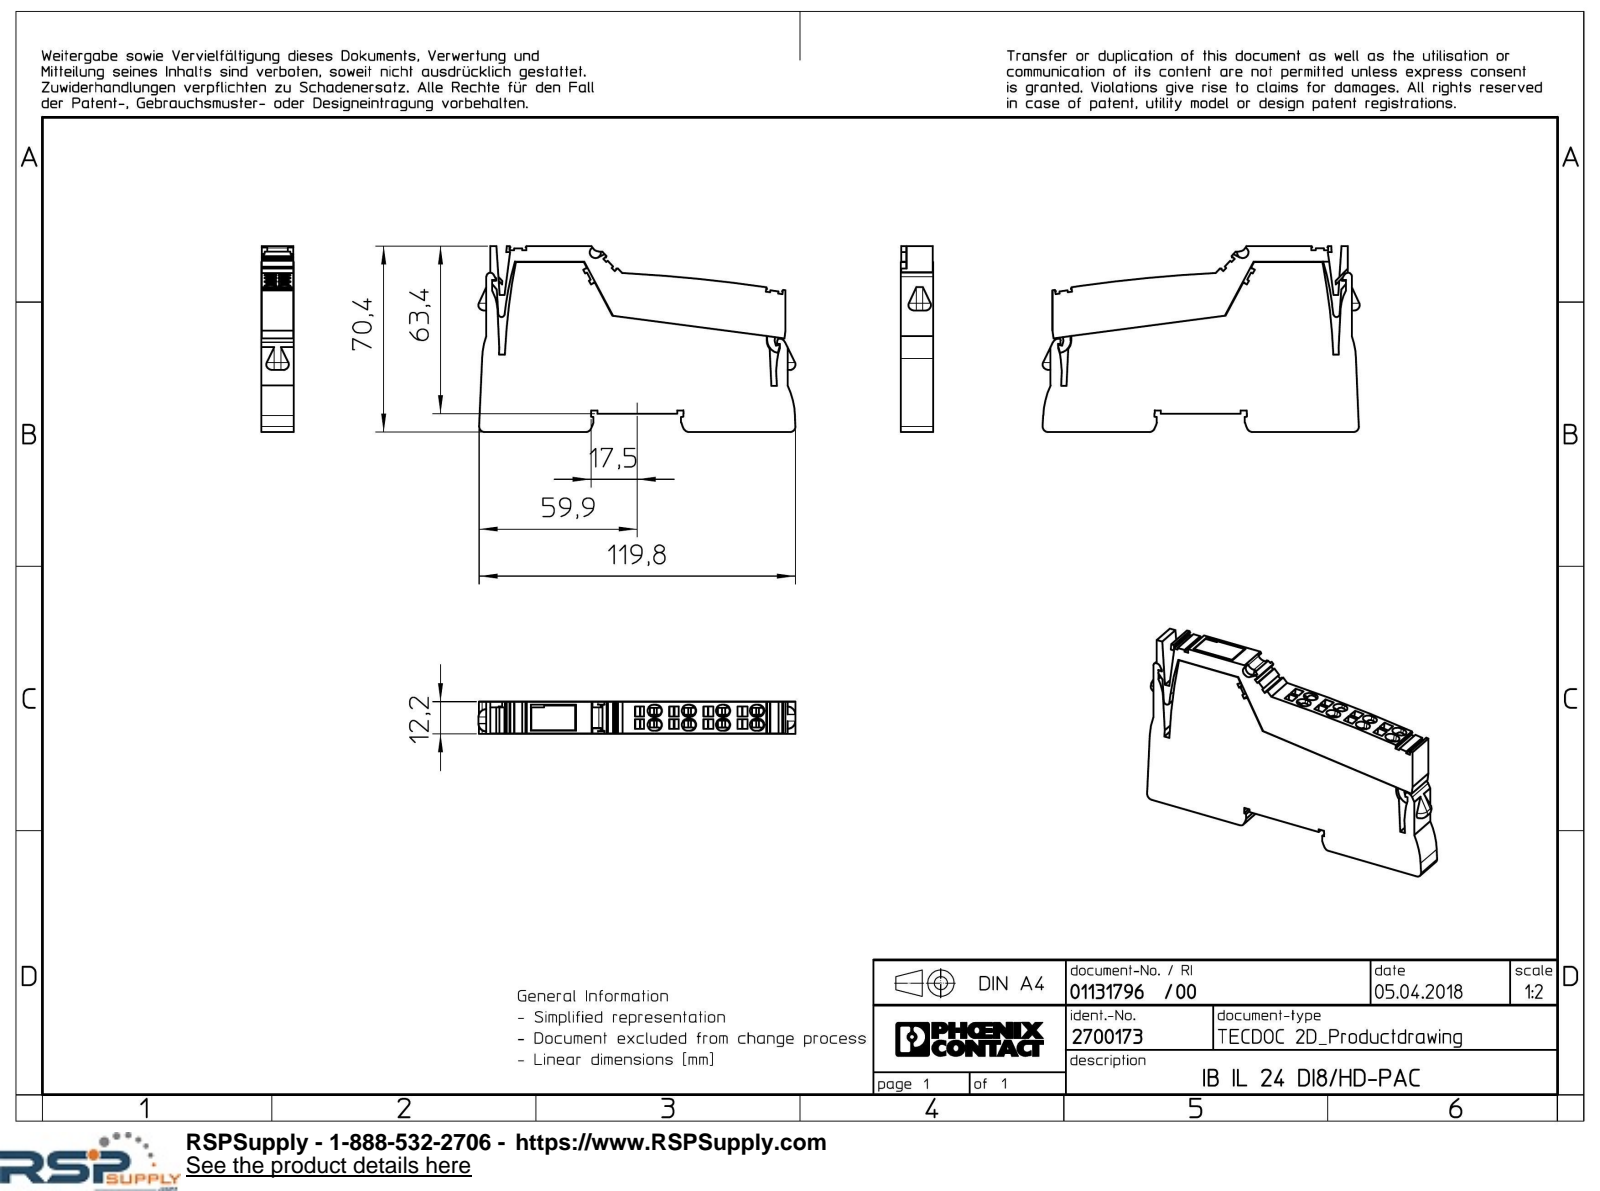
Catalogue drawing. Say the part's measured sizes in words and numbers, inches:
The part is named "L_L_2_GEH_GN_6021-select; L-L_LWL_HBU_AUSSEN-select; L-L_ST_GN_6021-select; IB_IL_24_DI8_HD_PAC-select". Its 3-D file was written by "Creo Elements/Direct Modeling 20.1A 29-Sep-2018 (C) Parametric Technology GmbH (AUTOMOTIVE_DESIGN)". It is 3 solids with 598 faces: 501 planar, 61 cylindrical and 36 other. Overall it measures 4.729 by 2.773 by 0.478 inches. Its volume is 4.888 cubic inches and its surface area 43.53 square inches. Round holes: 6 of diameter 0.047. Partial cylindrical surfaces (rounded edges, fillets, slot ends): 16 of radius 0.089, 6 of radius 0.079, 2 of radius 0.006, 2 of radius 0.024, 2 of radius 0.335, 2 of radius 0.374, 2 of radius 0.657, 2 of radius 1.181. The main face-to-face distances are 0.478, 0.476, 0.474, 0.472, 1.023, 0.13, 0.189, 2.535, 0.511, 0.028. The hole center spacings are 0.512, 0.546, 0.189, 1.024, 1.041.
